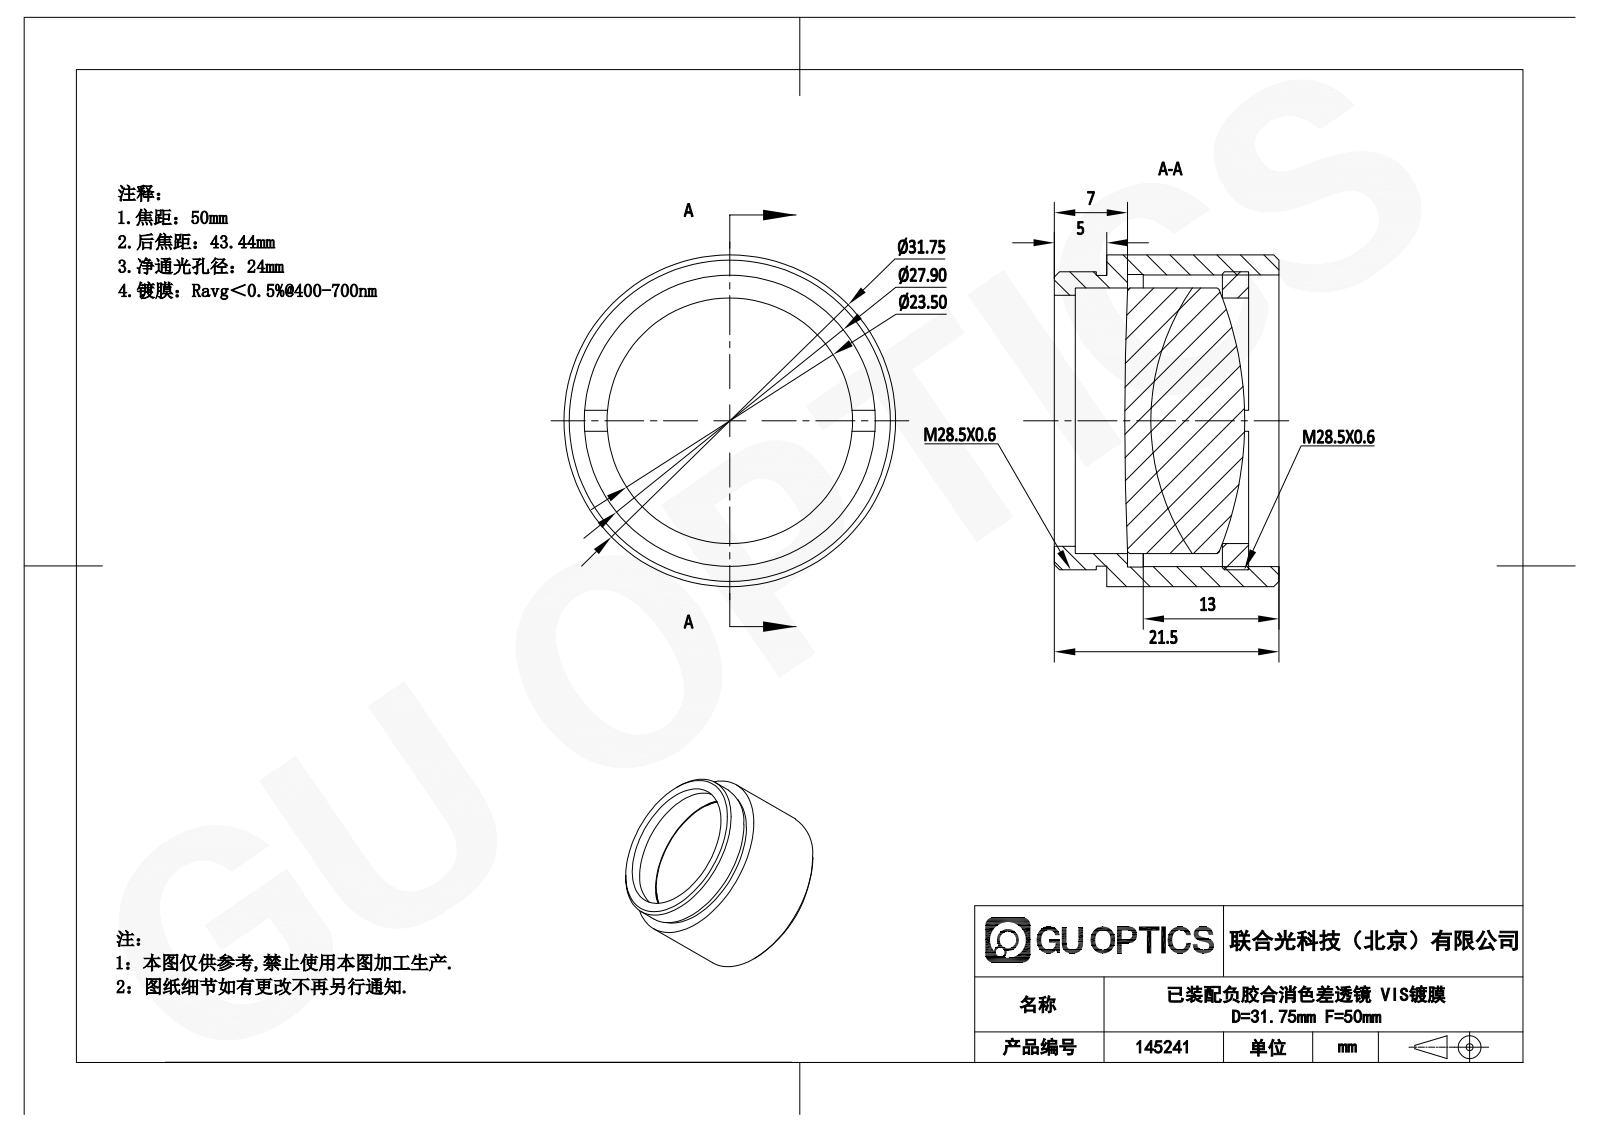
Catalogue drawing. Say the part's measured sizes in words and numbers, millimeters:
The part is named "GL31-025B-050-VIS_Solidworks; M28.5x0.6ѹȦ; APD-ML25-050-VIS". Its 3-D file was written by "SolidWorks 2022 (AUTOMOTIVE_DESIGN)". It is 4 solids with 56 faces: 16 planar, 22 cylindrical and 18 other. Overall it measures 31.76 by 31.76 by 21.5 millimeters. Its volume is 9 518 cubic millimeters and its surface area 8 243 square millimeters. Round holes: 1 of diameter 23.5, 1 of diameter 24, 1 of diameter 27.9, 1 of diameter 28. Round bosses or shafts: 1 of diameter 31.76, 1 of diameter 28.5, 1 of diameter 27.8, 1 of diameter 25.4. The main face-to-face distances are 2, 5, 2.5, 11.08, 13.58, 16.08, 18.58, 21.5, 16.5, 5.42.
